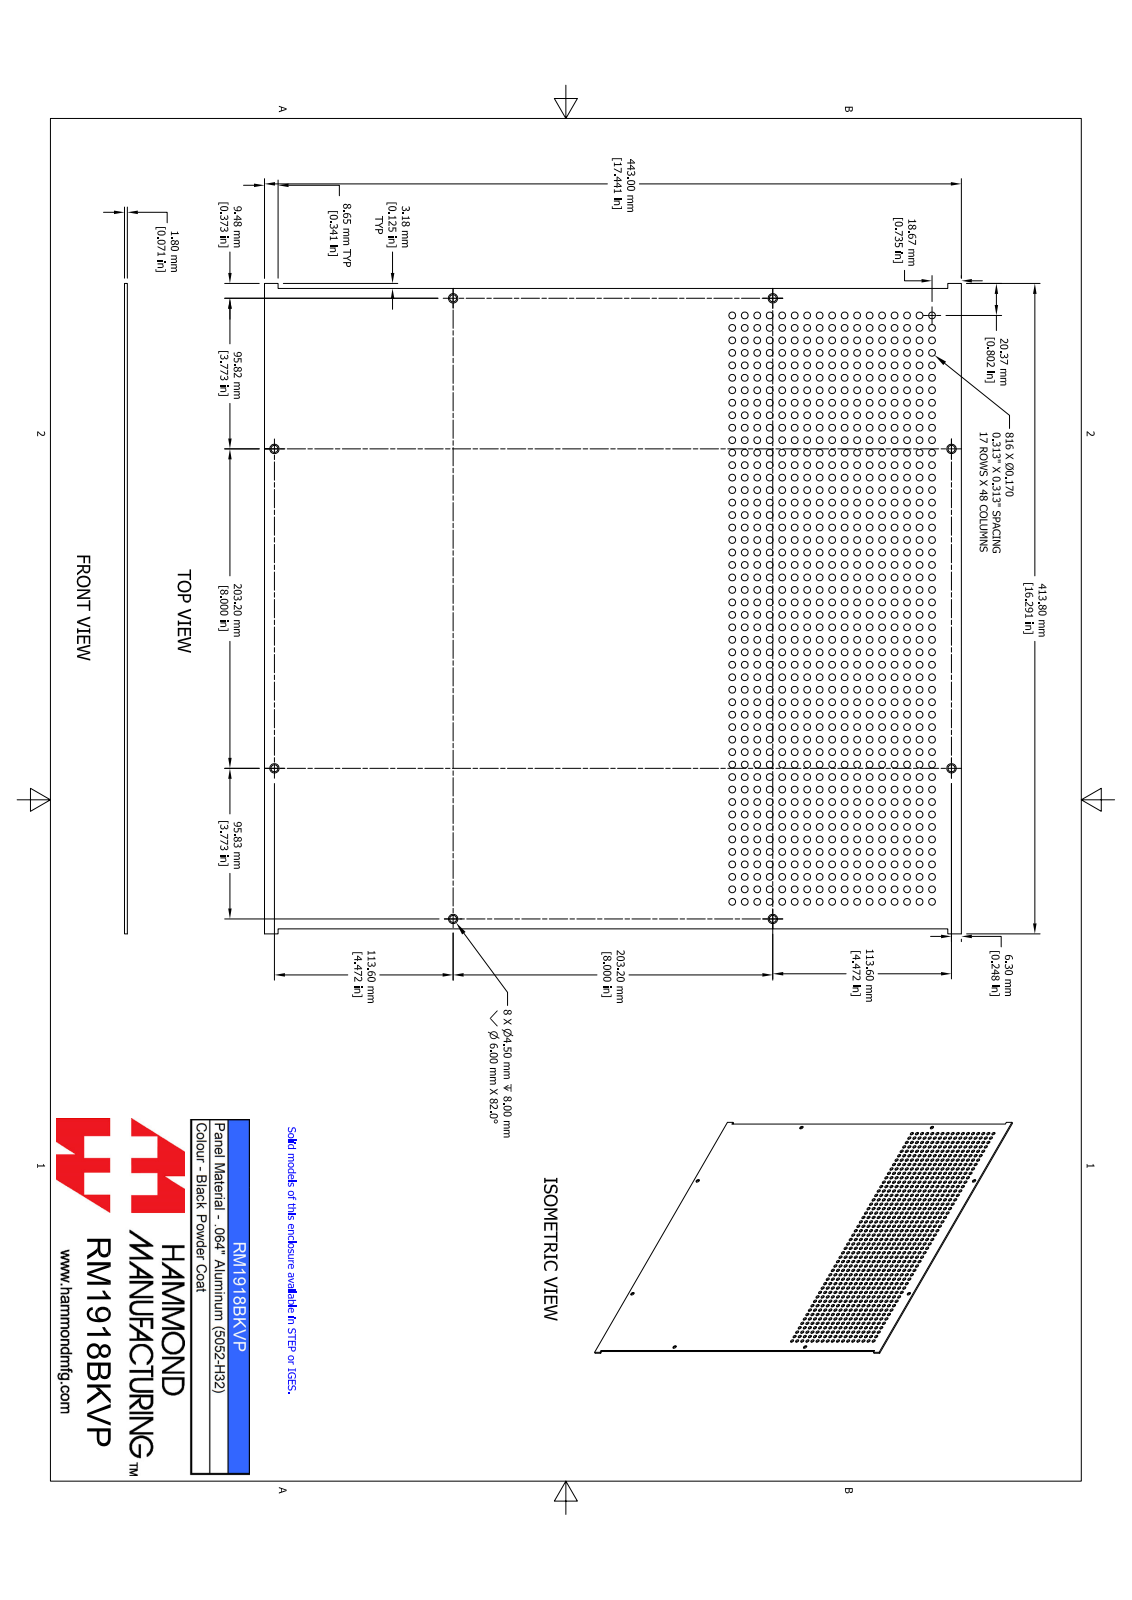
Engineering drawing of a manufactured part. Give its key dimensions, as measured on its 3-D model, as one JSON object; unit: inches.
{"part_name": "RM1918BKVP", "step_written_by": "SolidWorks 2021 (AUTOMOTIVE_DESIGN)", "units": "inches", "bodies": {"solids": 1, "faces": 846, "planar": 14, "cylindrical": 824, "other": 8}, "overall_size": [17.441, 16.291, 0.071], "volume_in3": 18.51, "surface_area_in2": 558.4, "round_holes": [[0.17, 816], [0.177, 8]], "face_to_face_distances": [0.071, 16.041, 17.441, 0.125, 16.167, 16.291, 16.166, 0.125, 0.341, 17.1], "hole_center_spacings": [1.25, 0.313, 0.937, 2.5, 1.563, 2.187, 0.625, 0.625]}
